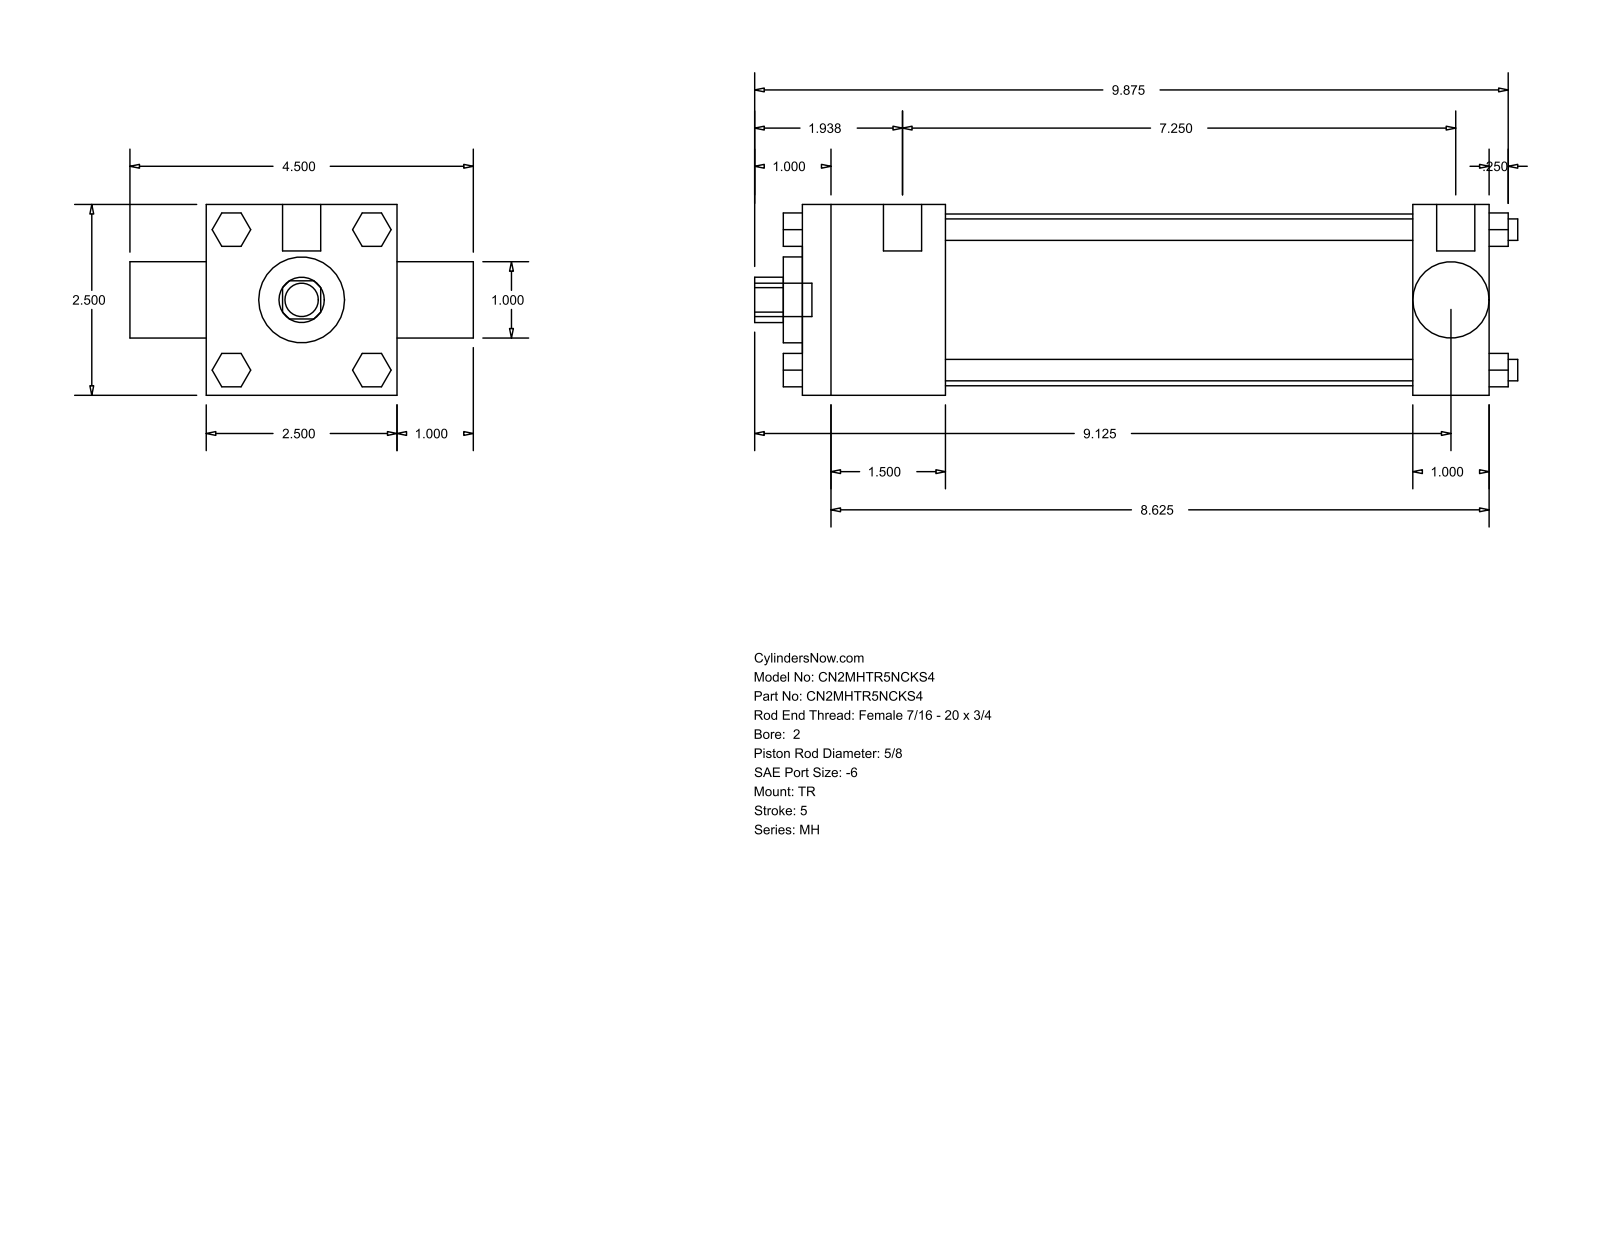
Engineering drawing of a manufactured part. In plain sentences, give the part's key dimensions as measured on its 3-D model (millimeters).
The part is named "MH_TR__0200_0.625". Its 3-D file was written by "GSSL Pune (CONFIG_CONTROL_DESIGN)". It is 0 solids with 120 faces: 92 planar, 28 cylindrical and 0 other. Overall it measures 254 by 114.3 by 63.5 millimeters. Round holes: 1 of diameter 15.88, 1 of diameter 25.35, 1 of diameter 28.57, 1 of diameter 57.15. Round bosses or shafts: 4 of diameter 7.14, 3 of diameter 5.56, 2 of diameter 12.7, 1 of diameter 11.11. Partial cylindrical surfaces (rounded edges, fillets, slot ends): 1 of radius 7.54. The main face-to-face distances are 63.5, 228.59, 25.4, 47.62, 203.19, 155.57, 180.97, 6.35, 88.9, 234.94.
